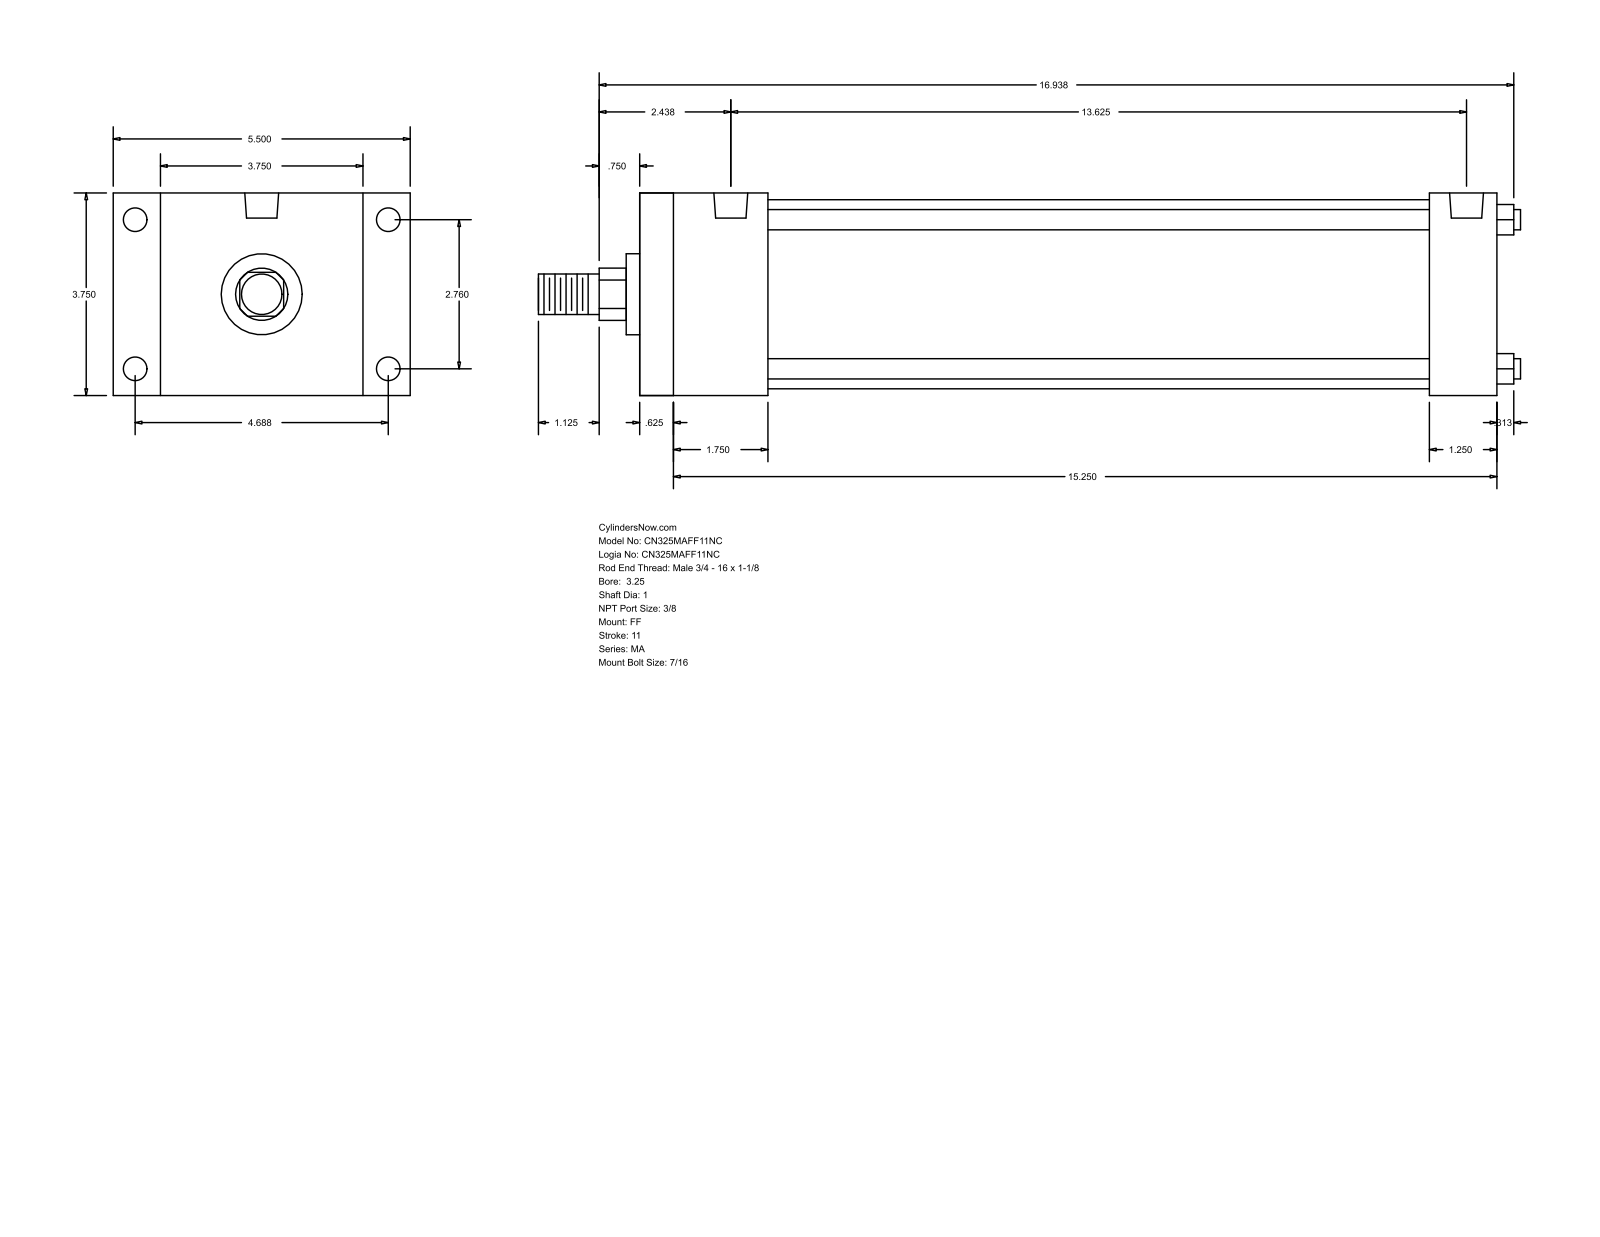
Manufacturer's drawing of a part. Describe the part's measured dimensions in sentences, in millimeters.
The part is named "MA_FF__0325_1". Its 3-D file was written by "GSSL Pune (CONFIG_CONTROL_DESIGN)". It is 0 solids with 92 faces: 64 planar, 28 cylindrical and 0 other. Overall it measures 461.96 by 139.7 by 95.25 millimeters. Round holes: 8 of diameter 11.11, 2 of diameter 15.93. Round bosses or shafts: 4 of diameter 9.53, 1 of diameter 88.9, 1 of diameter 38.1, 1 of diameter 25.4, 1 of diameter 19.05. Partial cylindrical surfaces (rounded edges, fillets, slot ends): 1 of radius 12.29. The main face-to-face distances are 95.24, 403.22, 15.87, 387.35, 22.23, 117.47, 60.33, 371.47, 44.46, 355.6. The hole center spacings are 4.76, 70.1, 119.06, 138.16, 336.56, 341.32, 346.08.
